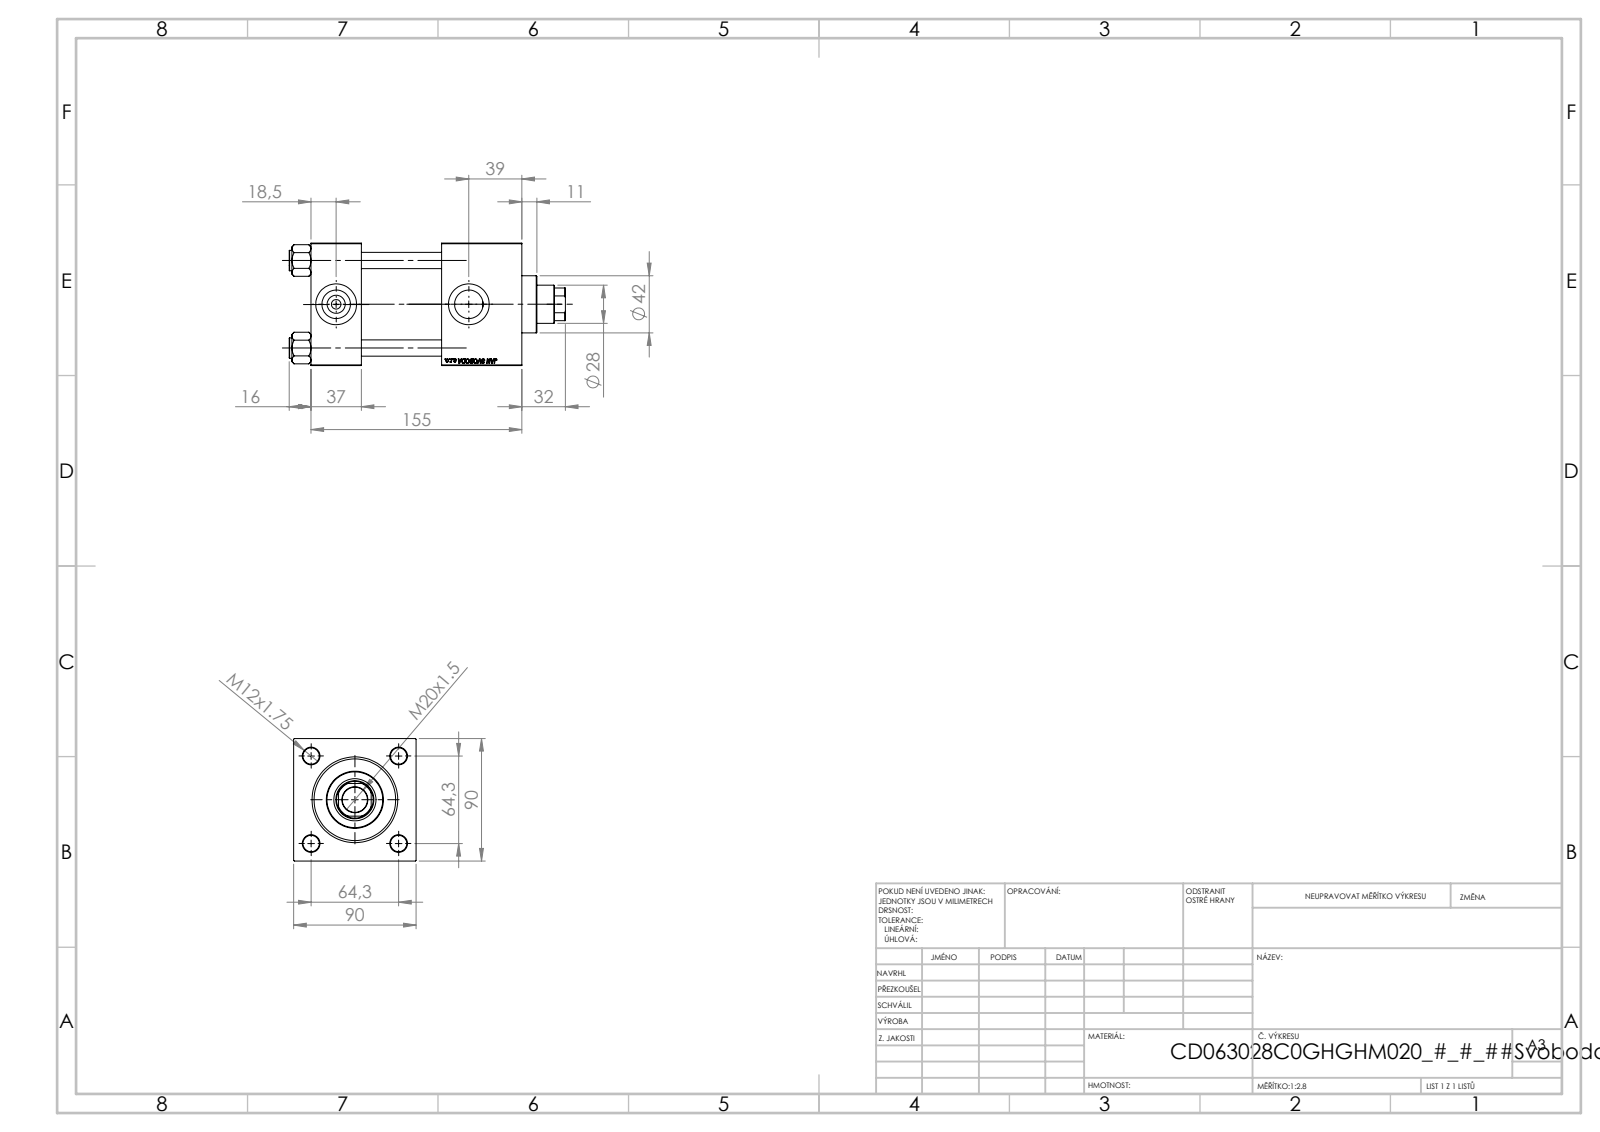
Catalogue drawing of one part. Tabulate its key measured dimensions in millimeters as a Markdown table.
| quantity | value |
| --- | --- |
| part name | V215CD_VCP_C; NUT_M5_V215CD_C; V215CD_C_TYCINKA; V215CD_VC_C (+1 more) |
| STEP written by | SolidWorks 2019 (CONFIG_CONTROL_DESIGN) |
| units | millimeters |
| bodies | 11 solids, 1148 faces (526 planar, 86 cylindrical, 536 other) |
| overall size | 203 × 90 × 90 |
| volume | 946 885 mm³ |
| surface area | 179 128 mm² |
| round holes (diameter × count) | 12 × 4, 7 × 2, 20.96 × 2, 30 × 2, 18.5 × 1, 28 × 1, 31 × 1, 50 × 1, 60 × 1, 63 × 1 |
| round bosses / shafts (diameter × count) | 15 × 4, 69 × 1, 42 × 1 |
| partial cylindrical surfaces (radius × count) | 13.5 × 1 |
| main face-to-face distances | 90, 59, 37, 155, 118, 96, 126.3, 89.3, 30.3, 28.7 |
| hole center spacings | 45.47, 64.3, 90.93, 97.5 |
